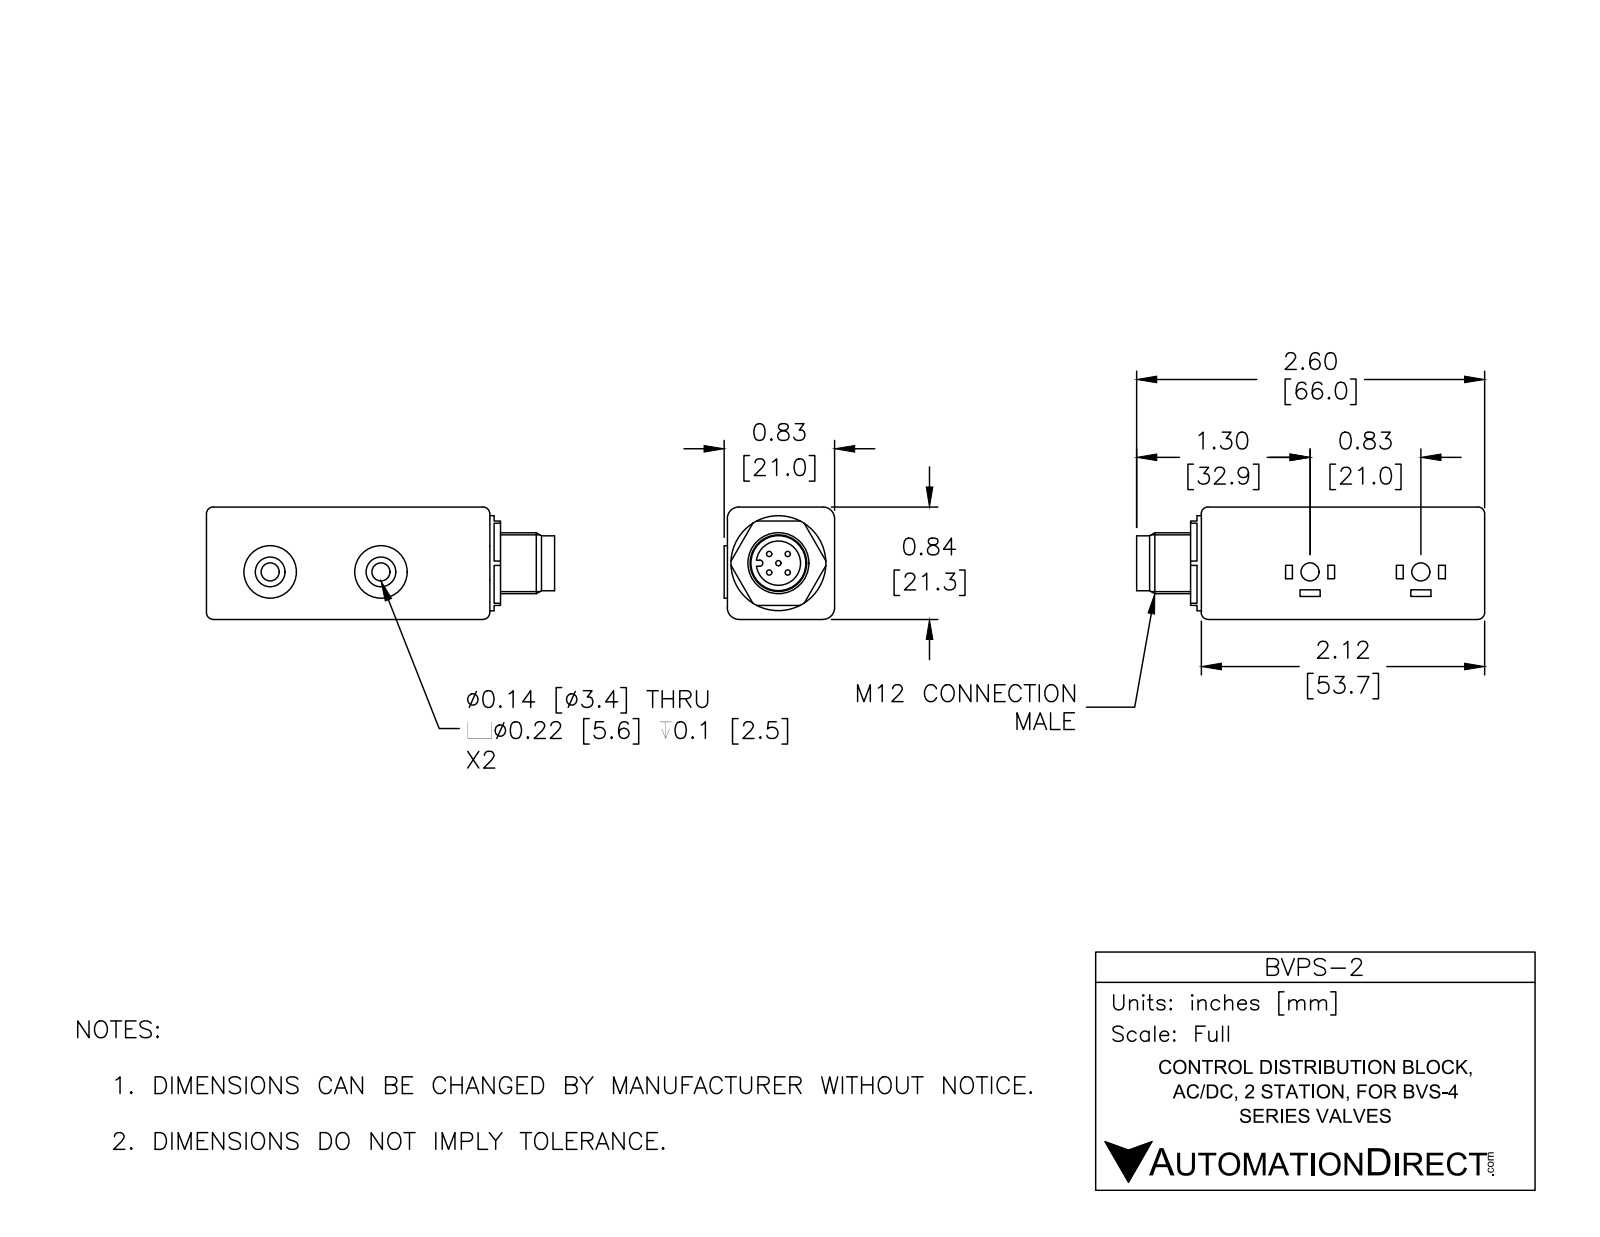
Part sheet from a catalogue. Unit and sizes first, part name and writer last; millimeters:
Units: millimetres
Overall size (bounding box): 66 × 21.3 × 21
Round holes (diameter × count): ⌀3.4 ×2, ⌀5.6 ×2, ⌀8.4 ×1
Round bosses / shafts (diameter × count): ⌀1 ×5, ⌀9.9 ×2, ⌀18 ×1, ⌀11.6 ×1, ⌀10.4 ×1
Partial cylindrical surfaces — rounded edges, fillets, slot ends (radius × count): R1.3 ×8, R2.2 ×4, R0.6 ×1
Main face-to-face distances: 21.3, 20.3, 55.8, 1.3, 0.6, 21, 2, 53.7, 21, 2.5
Hole centre spacings: 21
Volume: 23 500 mm³ · Surface area: 6 677 mm²
Bodies: 1 solid, 117 faces (63 planar, 44 cylindrical, 10 other)
Part name (STEP PRODUCT): BVPS-2
STEP written by: SolidWorks 2016 (AUTOMOTIVE_DESIGN)
